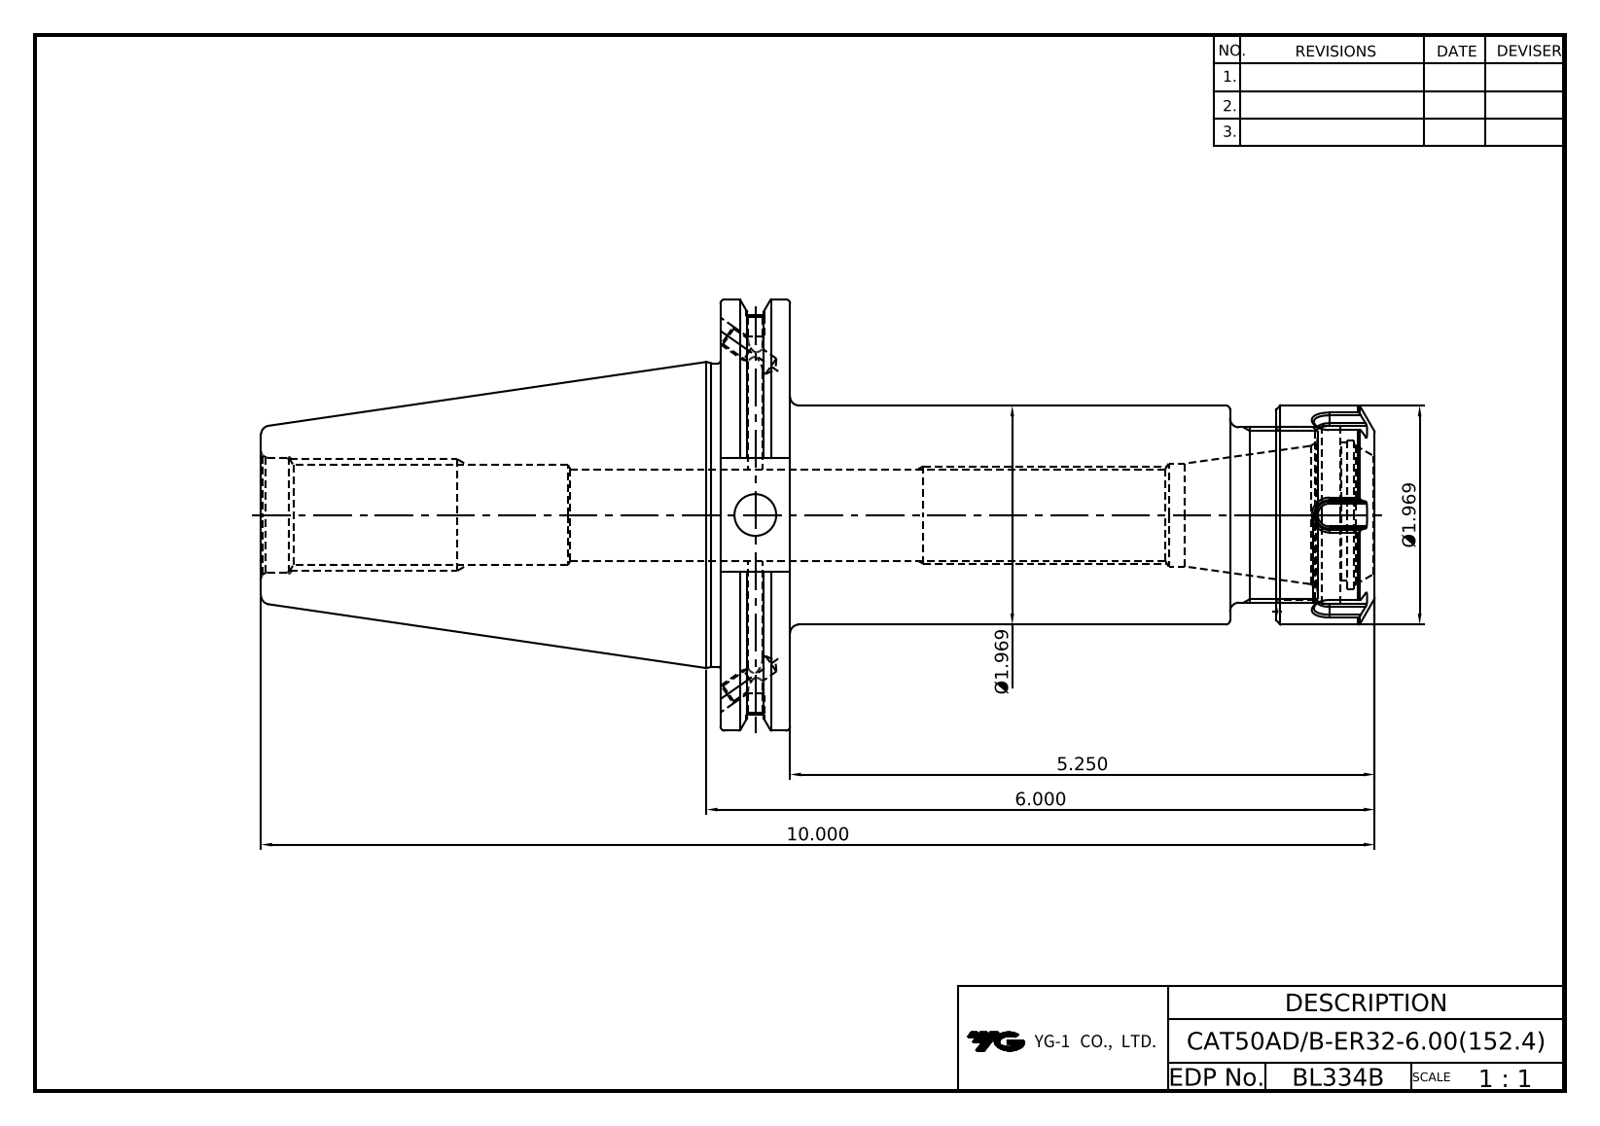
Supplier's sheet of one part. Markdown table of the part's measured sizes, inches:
| quantity | value |
| --- | --- |
| part name | BL334B-CAT50ADB-ER32-6_0; ER32NUT_3D_20140326; BL334B-CAT50ADB-ER32-6_0_ASM |
| STEP written by | PRO/ENGINEER BY PARAMETRIC TECHNOLOGY CORPORATION, 2012130 (CONFIG_CONTROL_DESIGN) |
| units | inches |
| bodies | 2 solids, 242 faces (76 planar, 84 cylindrical, 82 other) |
| overall size | 10 × 3.874 × 3.717 |
| volume | 31.23 in³ |
| surface area | 126.8 in² |
| round holes (diameter × count) | 0.197 × 5, 0.165 × 3, 0.039 × 1, 0.394 × 1, 0.823 × 1, 0.898 × 1, 0.926 × 1, 1.031 × 1, 1.067 × 1, 1.236 × 1, 1.331 × 1, 1.52 × 1 |
| round bosses / shafts (diameter × count) | 3.874 × 1, 3.594 × 1, 2.726 × 1, 1.969 × 1, 1.968 × 1, 1.575 × 1, 1.574 × 1 |
| partial cylindrical surfaces (radius × count) | 0.02 × 12 |
| main face-to-face distances | 0.625, 5.875, 5.25, 4.989, 4.364, 0.886, 5.564, 4.939, 0.575, 0.311 |
| hole center spacings | 0.031, 0.866, 0.898 |
